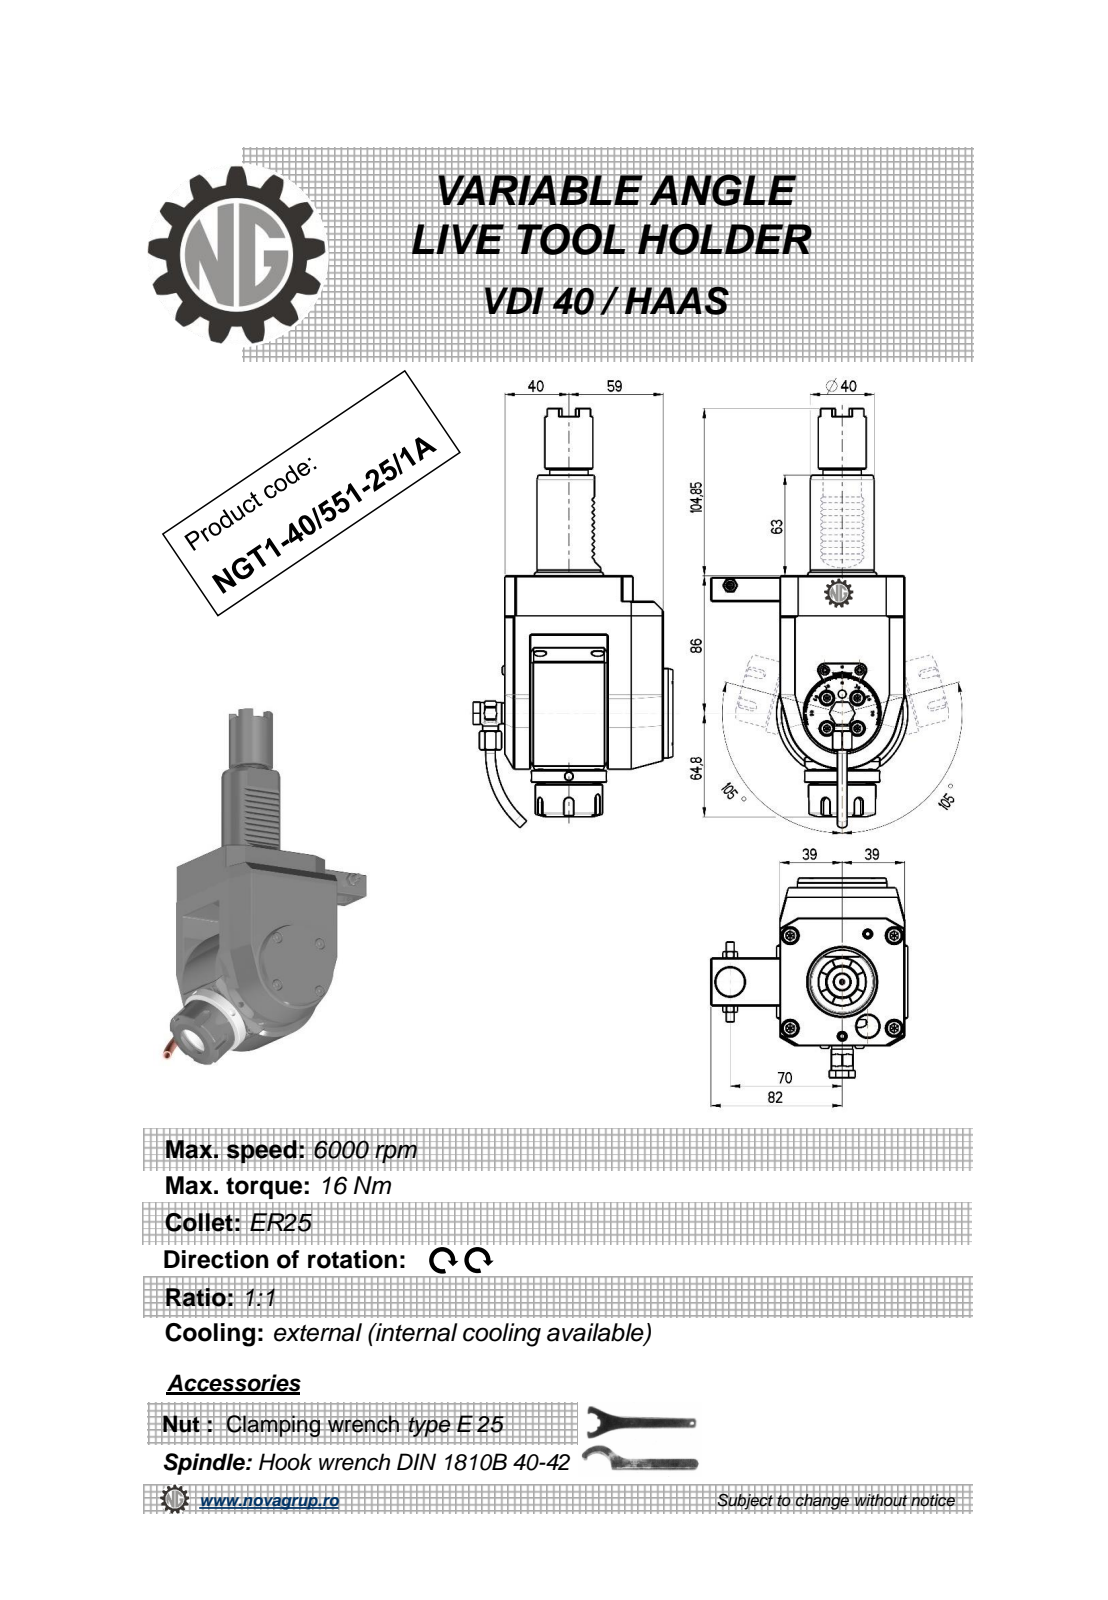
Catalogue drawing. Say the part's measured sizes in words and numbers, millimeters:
The part is named "NGT1_40_551_25_1A". Its 3-D file was written by "PRO/ENGINEER BY PARAMETRIC TECHNOLOGY CORPORATION, 2010280 (CONFIG_CONTROL_DESIGN)". It is 1 solid with 601 faces: 266 planar, 140 cylindrical and 195 other. Overall it measures 262.52 by 124.9 by 123 millimeters. Its volume is 950 184 cubic millimeters and its surface area 89 391 square millimeters. Round holes: 3 of diameter 4, 2 of diameter 5, 1 of diameter 3, 1 of diameter 4.2, 1 of diameter 6.2, 1 of diameter 9, 1 of diameter 9.5, 1 of diameter 11, 1 of diameter 18, 1 of diameter 20.3. Round bosses or shafts: 2 of diameter 10, 2 of diameter 6, 2 of diameter 5.7, 1 of diameter 82, 1 of diameter 56, 1 of diameter 47, 1 of diameter 42, 1 of diameter 40. Partial cylindrical surfaces (rounded edges, fillets, slot ends): 12 of radius 0.26, 10 of radius 0.3, 5 of radius 3, 4 of radius 0.5, 3 of radius 10, 2 of radius 1, 1 of radius 7.7, 1 of radius 35. The main face-to-face distances are 16, 37, 64, 99, 78, 6, 105, 1, 21, 25. The hole center spacings are 0.4, 39.45, 49, 49.4, 70, 85.45, 85.68, 106.3.
